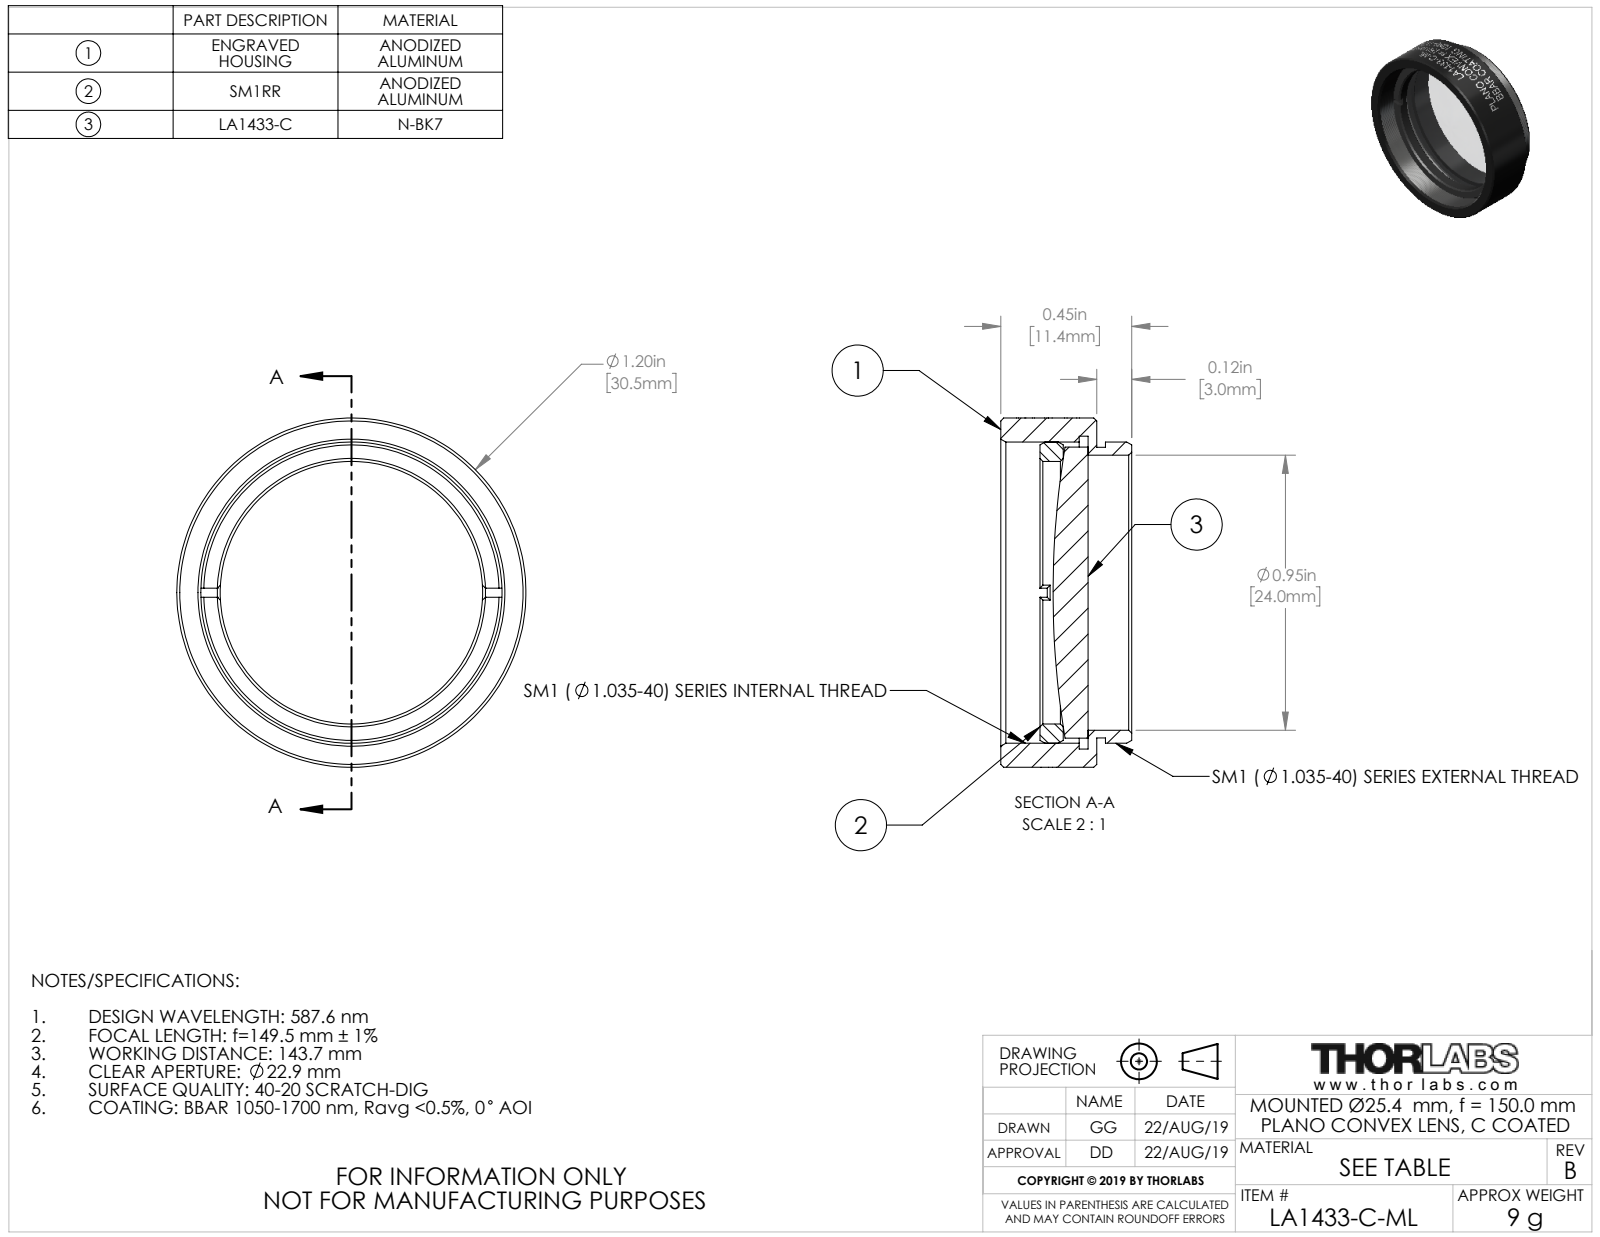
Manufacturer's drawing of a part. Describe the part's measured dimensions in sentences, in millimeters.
The part is named "24433-E0W". Its 3-D file was written by "SolidWorks 2018 (CONFIG_CONTROL_DESIGN)". It is 3 solids with 153 faces: 20 planar, 109 cylindrical and 24 other. Overall it measures 30.48 by 30.48 by 11.43 millimeters. Its volume is 3 361 cubic millimeters and its surface area 4 316 square millimeters. Round holes: 1 of diameter 22.91, 1 of diameter 24, 1 of diameter 27.3. Round bosses or shafts: 1 of diameter 30.48, 1 of diameter 26.29, 1 of diameter 25.4, 1 of diameter 25.37. The main face-to-face distances are 0.76, 8.38, 7.62, 3.43, 2.92, 2.16, 5.46, 4.95, 4.19, 2.03.
